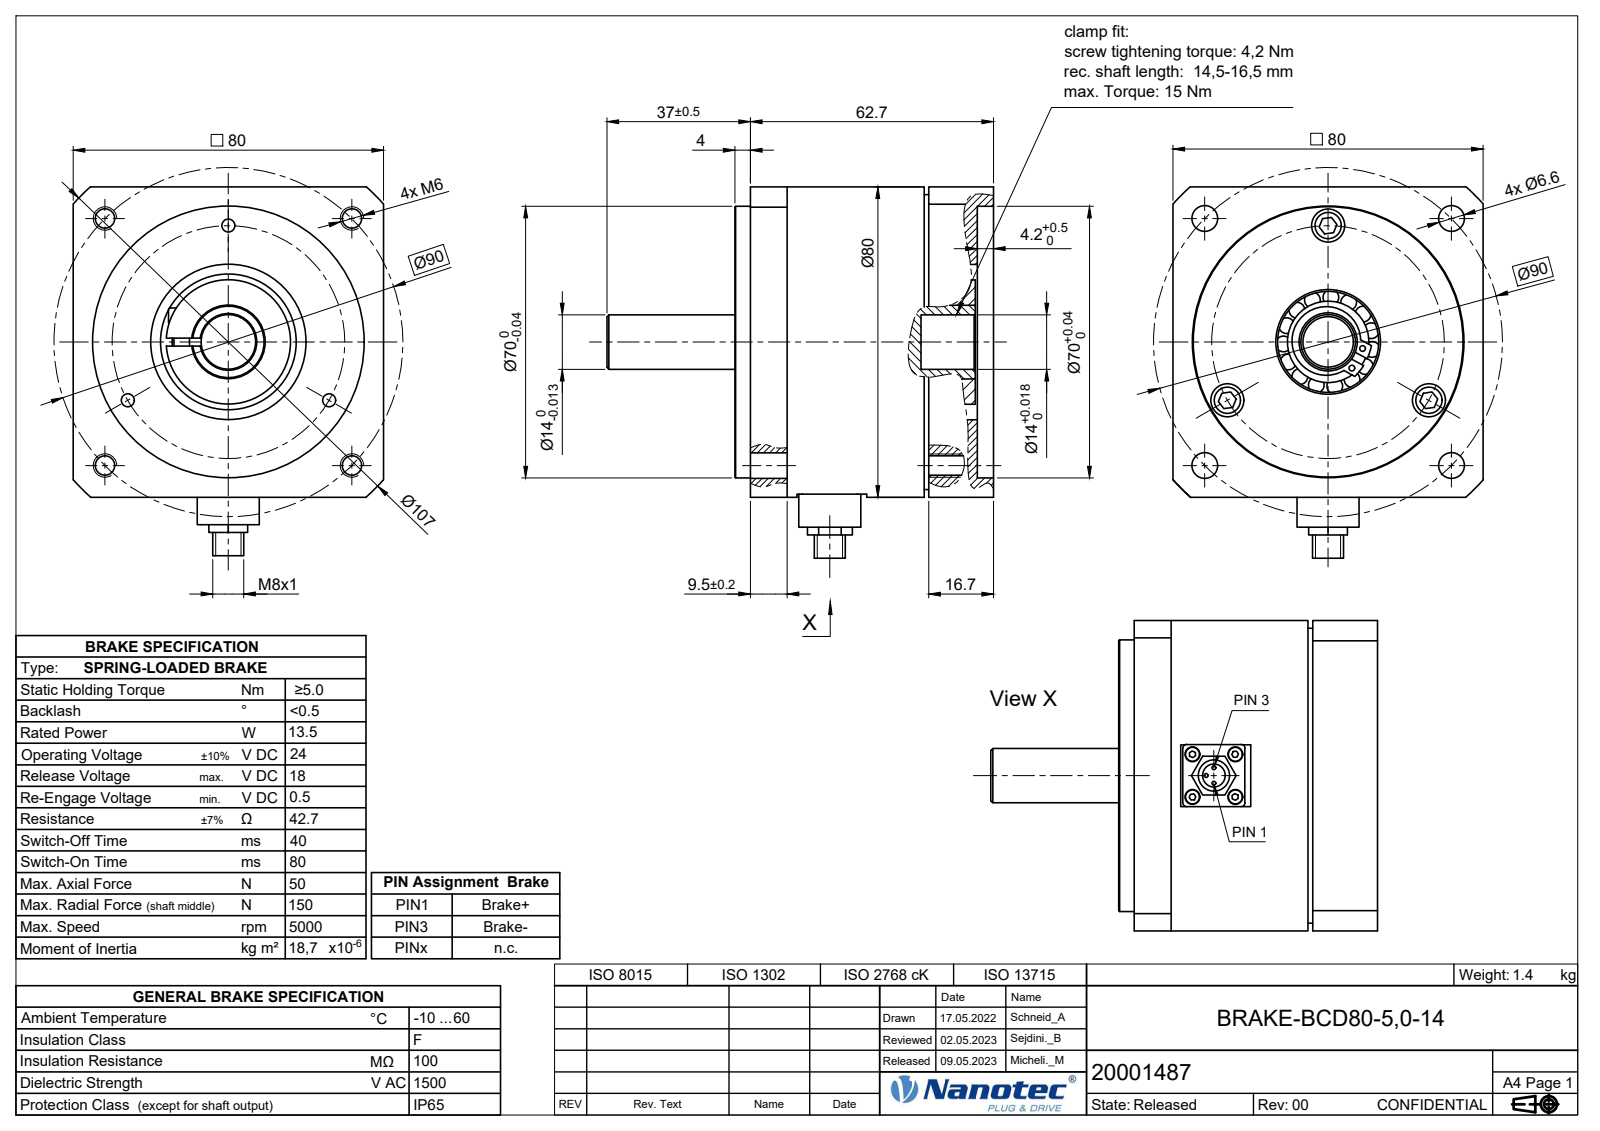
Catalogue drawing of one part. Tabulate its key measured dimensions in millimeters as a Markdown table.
| quantity | value |
| --- | --- |
| part name | BRAKE-BCD80-5,0-14 |
| STEP written by | Autodesk Inventor 2021 (AUTOMOTIVE_DESIGN) |
| units | millimeters |
| bodies | 1 solid, 132 faces (82 planar, 41 cylindrical, 9 other) |
| overall size | 104.81 × 104.81 × 99.7 |
| volume | 353 310 mm³ |
| surface area | 42 228 mm² |
| round holes (diameter × count) | 3.8 × 4, 5 × 4, 6.6 × 4, 5.88 × 1, 70 × 1, 76.2 × 1 |
| round bosses / shafts (diameter × count) | 3.62 × 4, 1 × 3, 80 × 1, 76 × 1, 71 × 1, 14 × 1, 8 × 1 |
| partial cylindrical surfaces (radius × count) | 1 × 4, 53.5 × 1 |
| main face-to-face distances | 80, 62.5, 66.7, 4.2, 4, 58.5, 62.7, 12.5, 46, 50 |
| hole center spacings | 7.78, 11, 63.64, 15.56, 44.99, 45, 90 |
